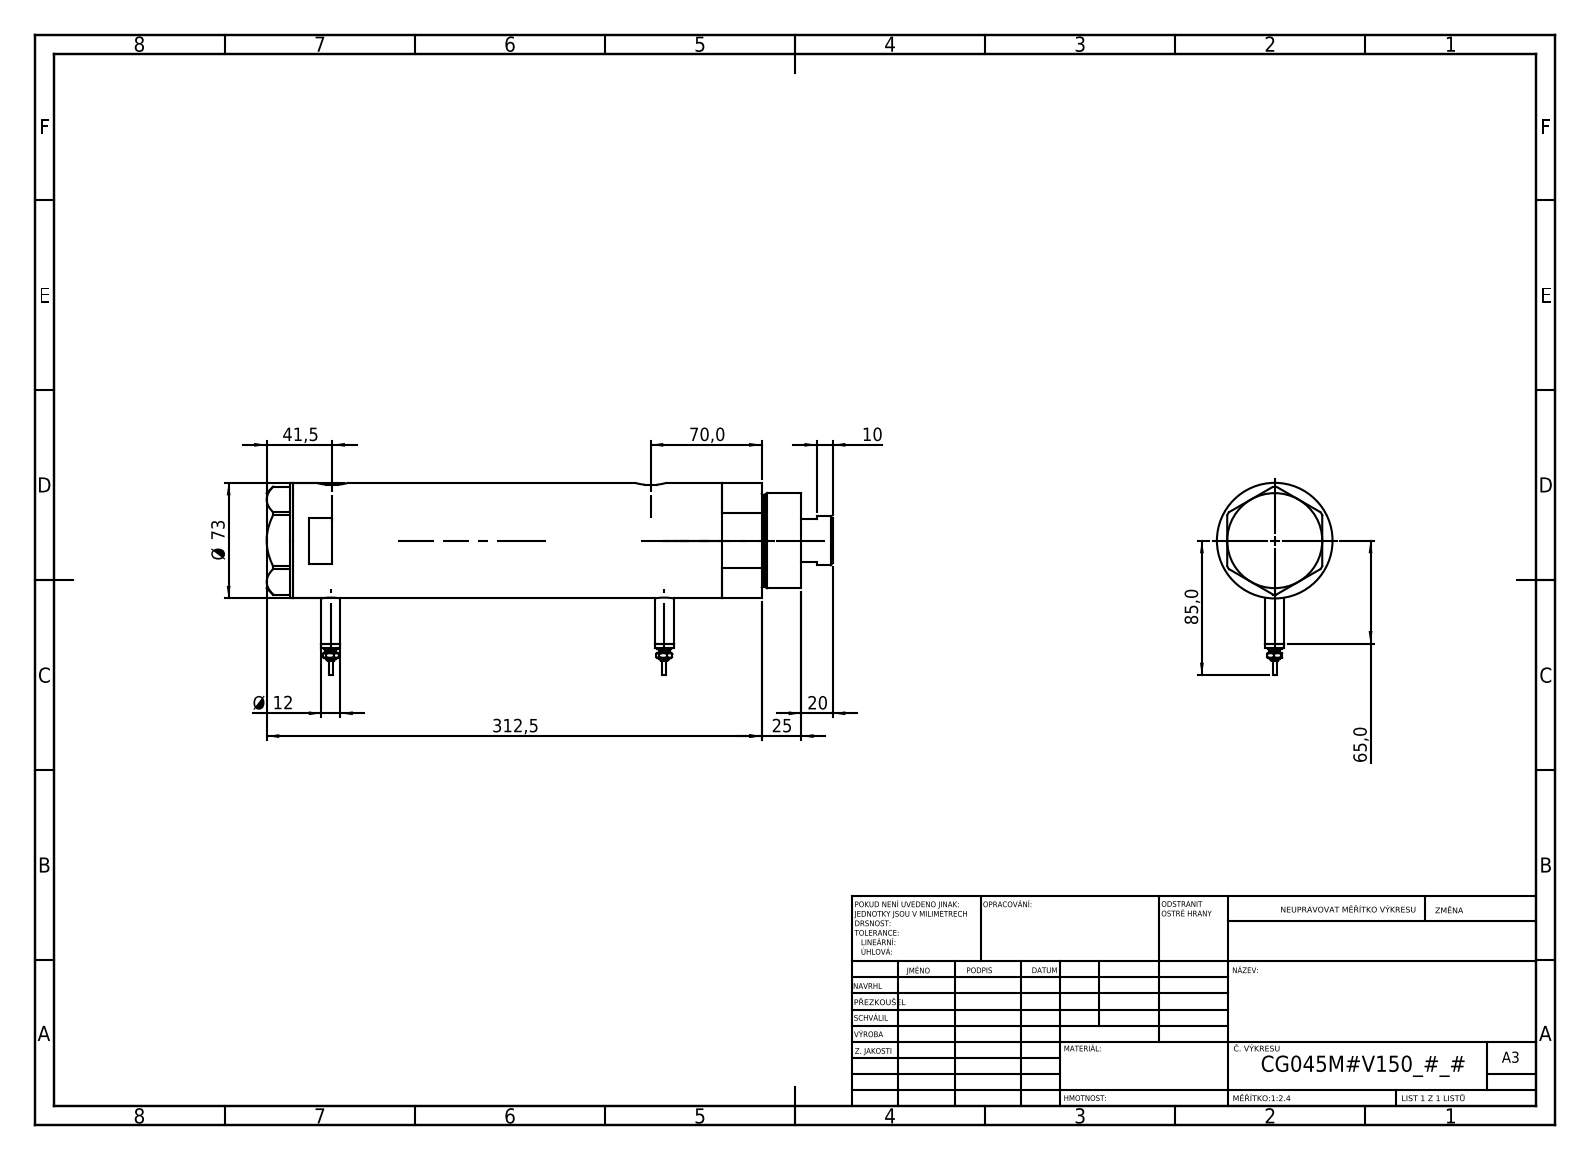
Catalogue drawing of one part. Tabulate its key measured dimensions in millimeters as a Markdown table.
| quantity | value |
| --- | --- |
| part name | V270CG_BACK; Switch; V270CG_MIDDLE; V270CG_VC (+1 more) |
| STEP written by | SolidWorks 2019 (CONFIG_CONTROL_DESIGN) |
| units | millimeters |
| bodies | 6 solids, 212 faces (77 planar, 71 cylindrical, 64 other) |
| overall size | 357.5 × 121.5 × 73 |
| volume | 1 253 000 mm³ |
| surface area | 201 414 mm² |
| round holes (diameter × count) | 12.5 × 2, 13.16 × 2, 10.5 × 1, 32 × 1, 33.5 × 1, 45 × 1, 48 × 1, 64 × 1 |
| round bosses / shafts (diameter × count) | 12 × 2, 9 × 2, 7 × 2, 4.5 × 2, 2.5 × 2, 73 × 1, 60 × 1, 58 × 1 |
| partial cylindrical surfaces (radius × count) | 10 × 2 |
| main face-to-face distances | 226, 26, 200, 16.5, 42.5, 242.5, 2, 321, 337.5, 295 |
| hole center spacings | 1, 8.5, 201, 202, 209.5, 210.5 |
